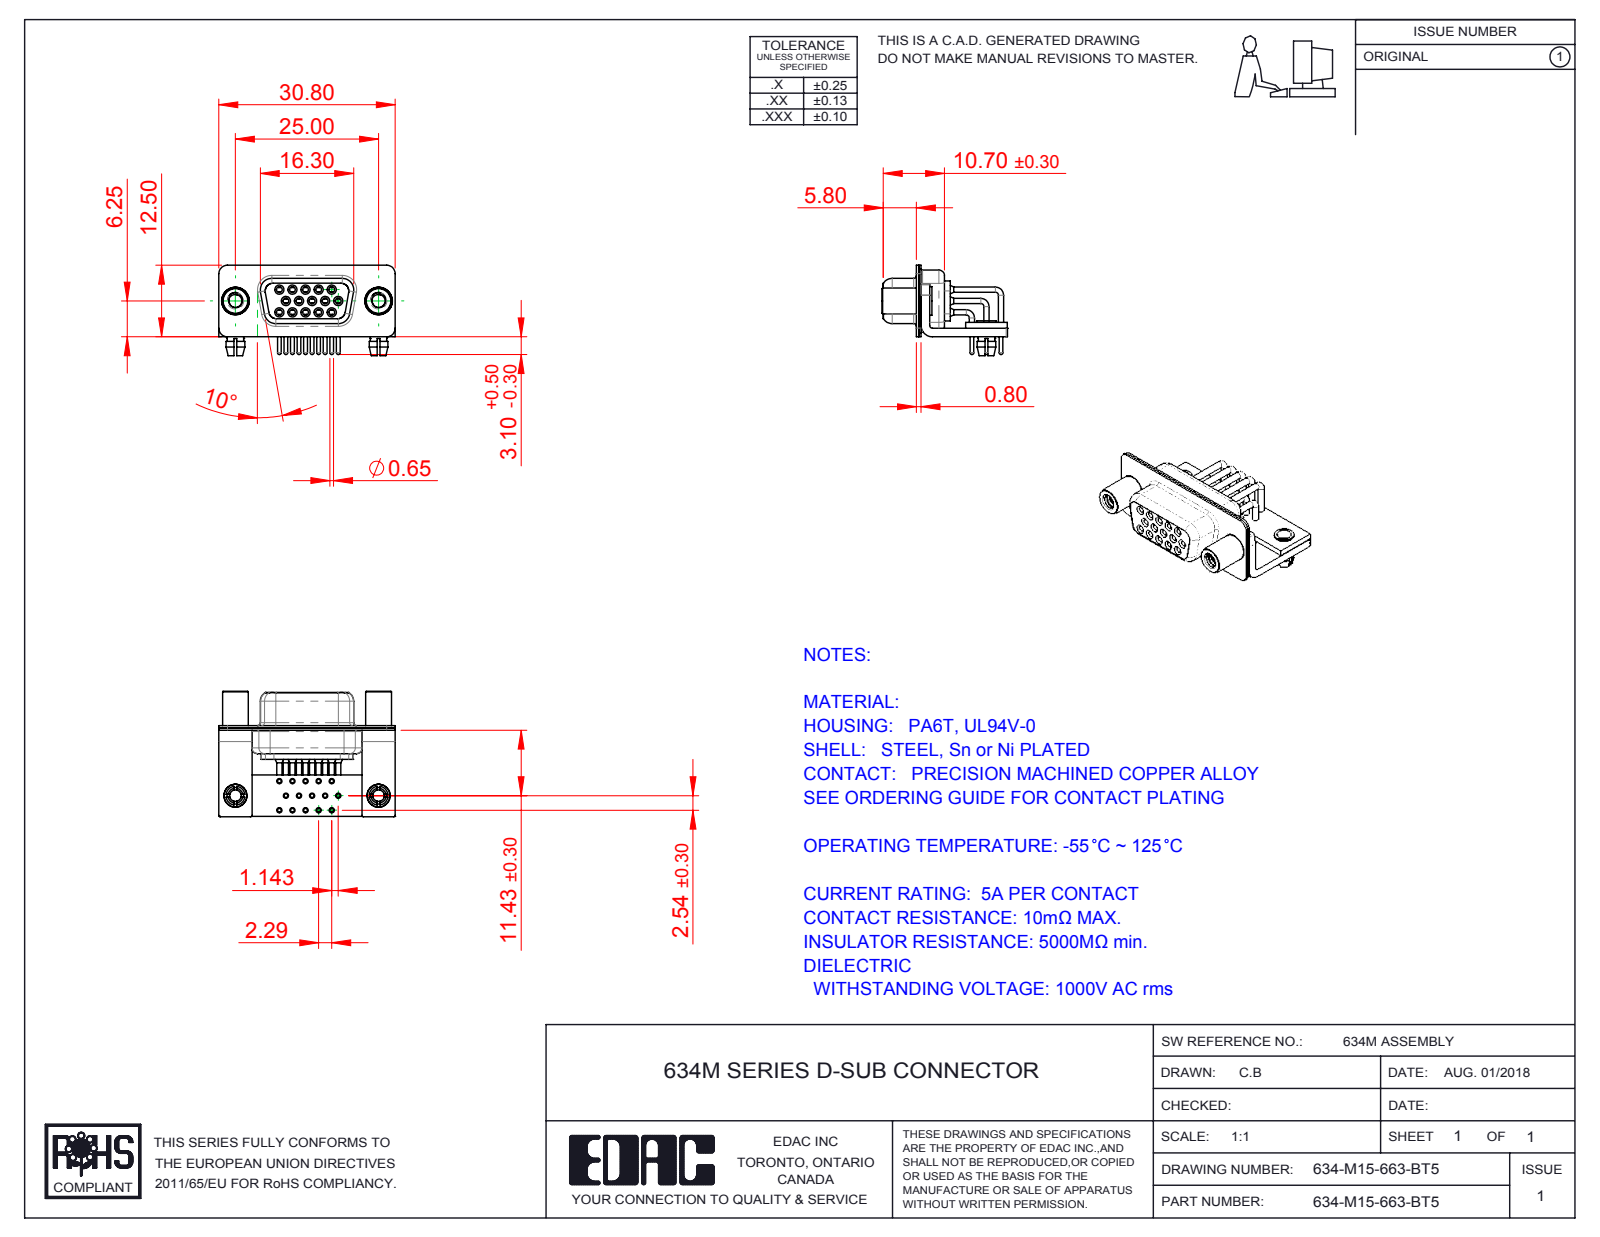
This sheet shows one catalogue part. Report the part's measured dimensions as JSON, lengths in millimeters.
{"part_name": "634M Board Lock; 634M Stabilizer Board_15 Contacts; 634M 4-40 Threaded Standoff; 634M Stabilizer Bracket (+7 more)", "step_written_by": "SolidWorks 2016 (CONFIG_CONTROL_DESIGN)", "units": "millimeters", "bodies": {"solids": 25, "faces": 1296, "planar": 368, "cylindrical": 608, "other": 320}, "overall_size": [30.8, 21.9, 15.8], "volume_mm3": 2389, "surface_area_mm2": 7381, "round_holes": [[2, 17], [0.9, 15], [1, 15], [1.1, 15], [1.7, 15], [1.8, 15], [2.26, 2], [2.5, 2], [3.2, 2], [4, 2], [4.8, 2]], "round_bosses_or_shafts": [[1.6, 15], [1.5, 15], [0.9, 15], [0.65, 15], [5, 2], [4.9, 2], [4.5, 2], [4, 2]], "partial_cylinders_radius": [[0.25, 16], [1.5, 16], [2, 13], [1.35, 8], [1.6, 8], [0.5, 5], [0.6, 4], [0.65, 4]], "face_to_face_distances": [0.4, 1.5, 0.8, 2.3, 1.9, 1, 9.35, 8.5, 1.45, 2.5], "hole_center_spacings": [2.29, 2.28, 4.57, 3.96, 4.27, 2.78, 6.05, 6.86]}
